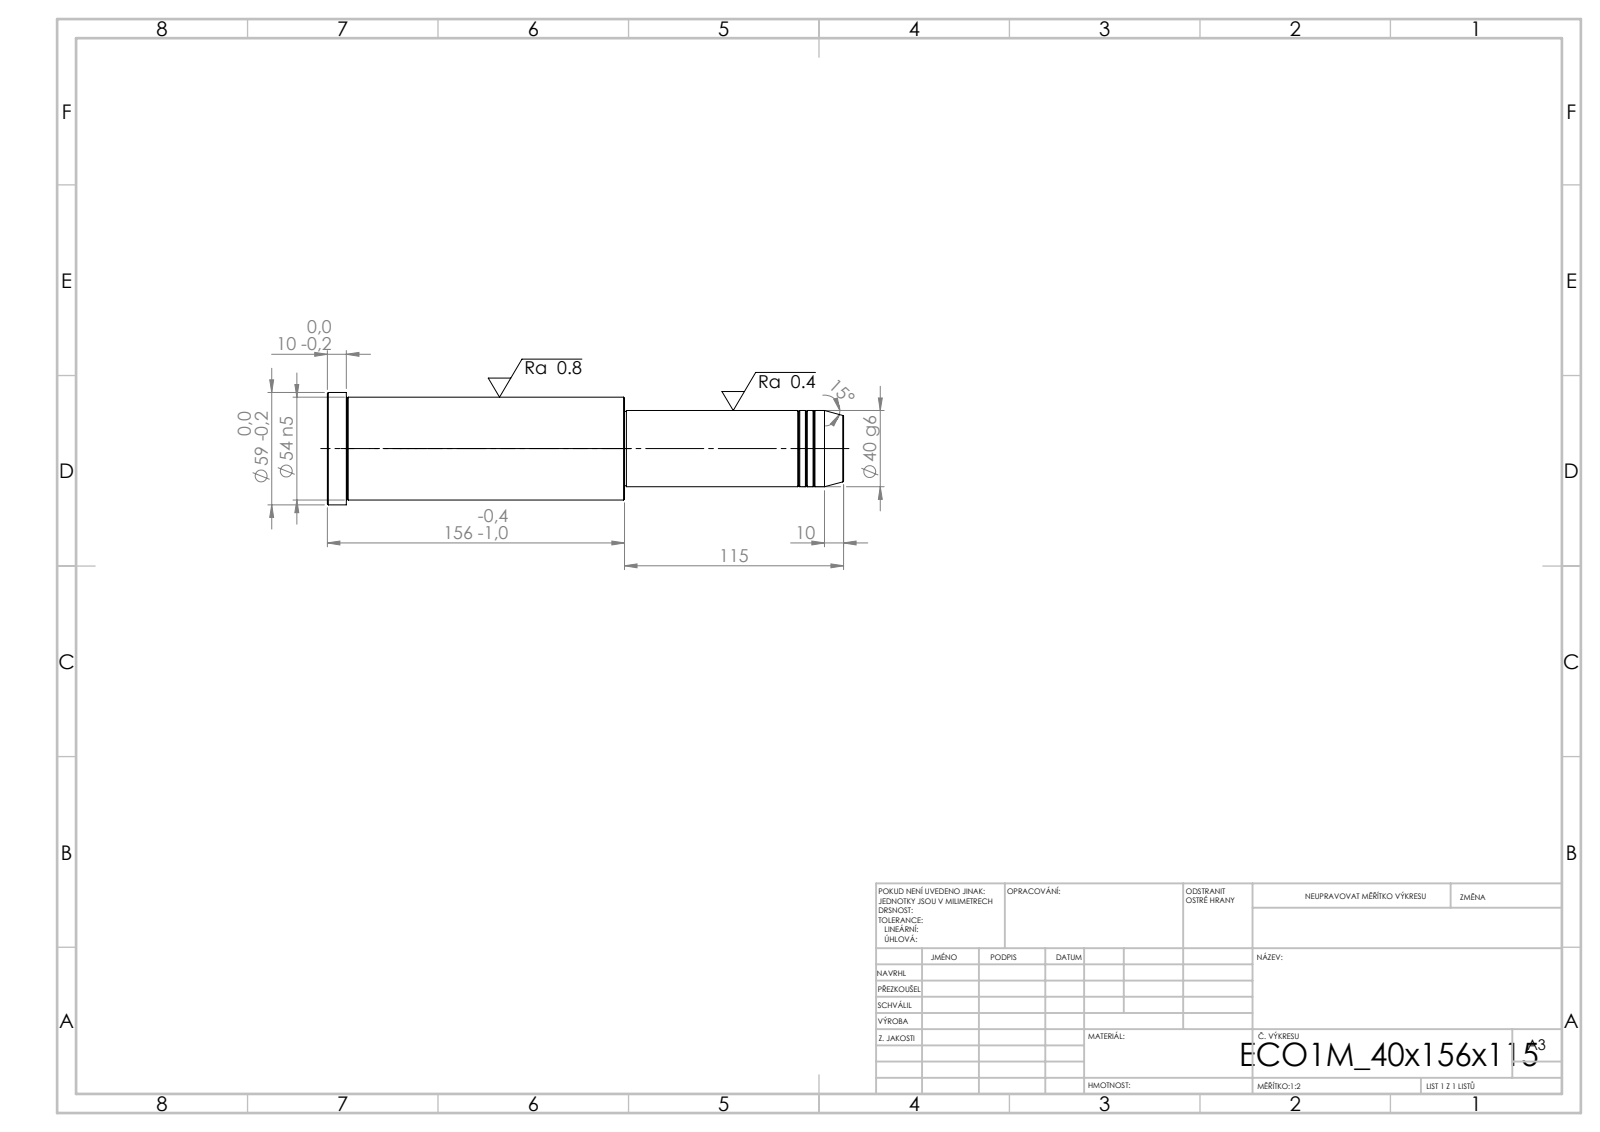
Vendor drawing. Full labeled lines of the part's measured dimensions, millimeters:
STEP written by: SolidWorks 2019 (CONFIG_CONTROL_DESIGN)
Units: millimetres
Bodies: 1 solid, 43 faces (5 planar, 14 cylindrical, 24 other)
Overall size (bounding box): 271 × 59 × 59
Volume: 504 295 mm³ · Surface area: 46 488 mm²
Round bosses / shafts (diameter × count): ⌀59 ×1, ⌀54 ×1, ⌀40 ×1, ⌀39 ×1
Main face-to-face distances: 156, 115, 271, 261, 146, 10, 114, 1, 147, 157
